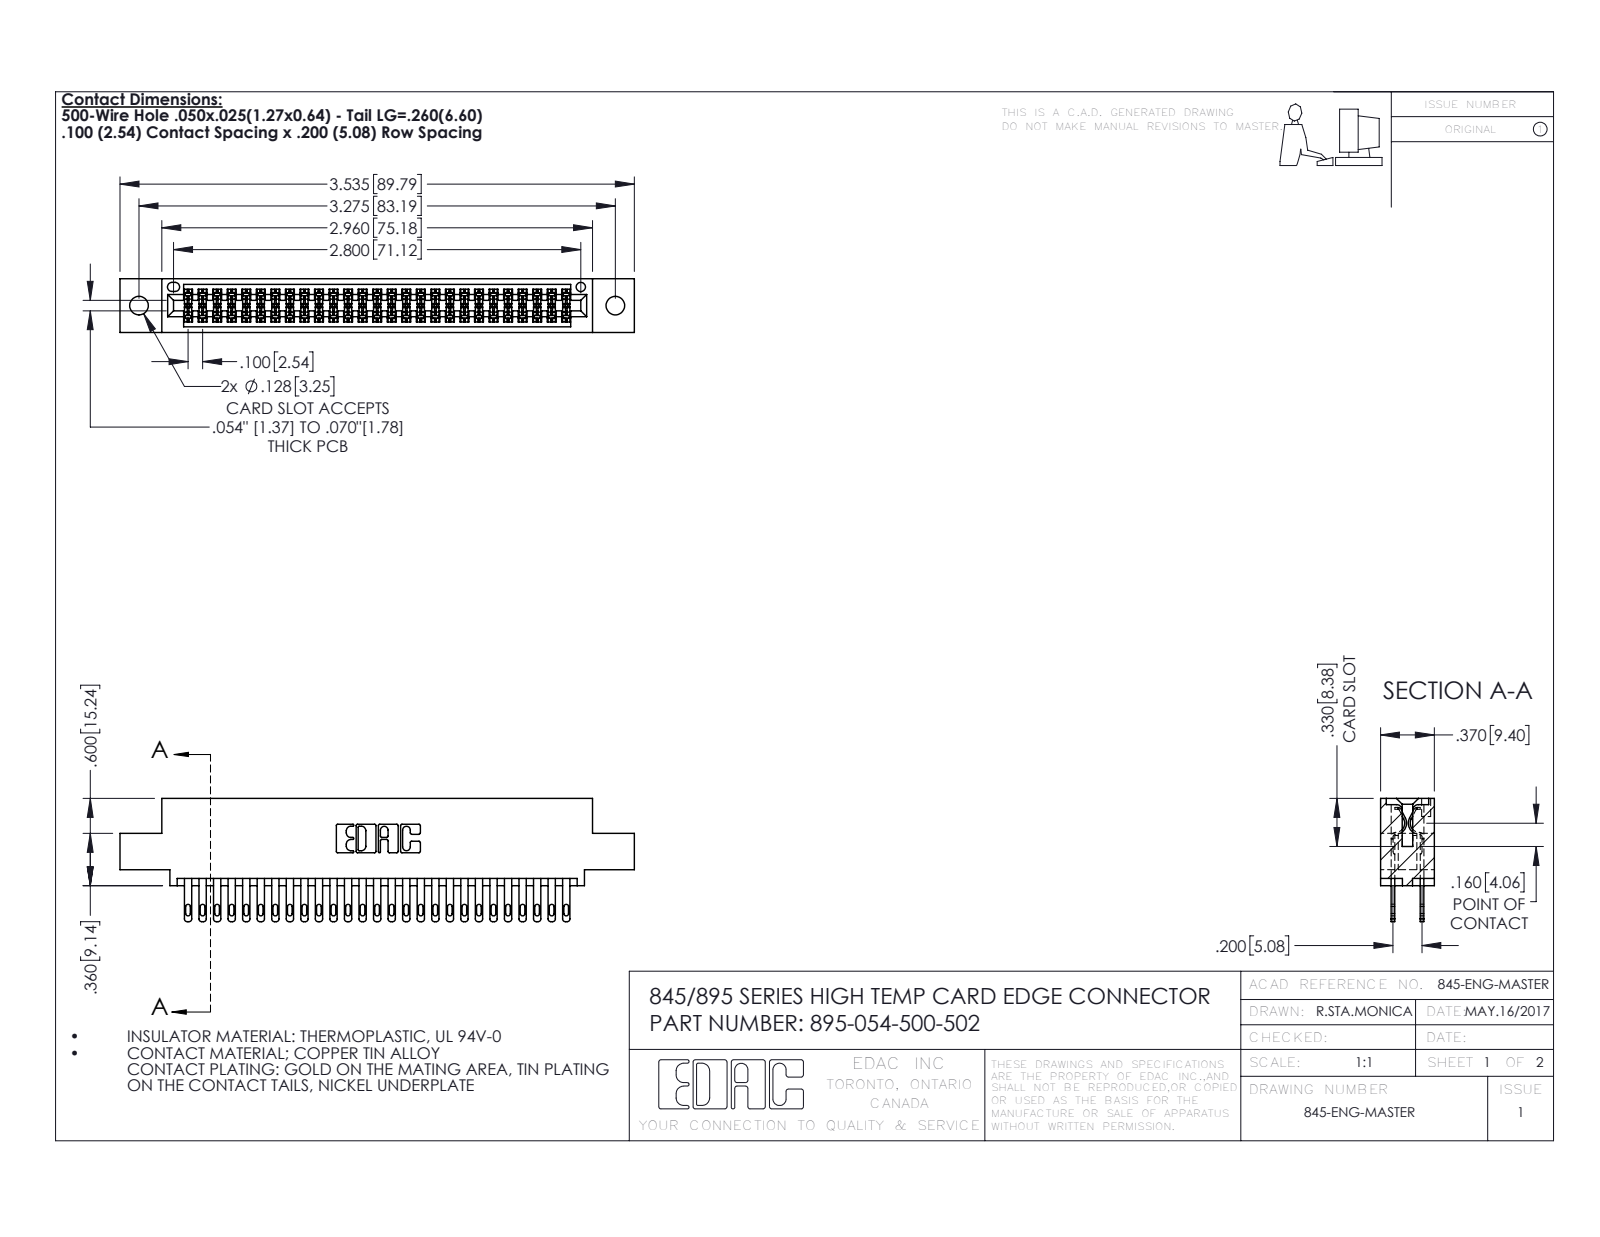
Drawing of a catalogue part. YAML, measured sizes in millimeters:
part_name: "845 Part_0.110 Offset - 0.128 Dia; 345-292-001_345-293-100; 895-054-500-502"
step_written_by: "SolidWorks 2020 (CONFIG_CONTROL_DESIGN)"
units: millimeters
bodies: {solids: 55, faces: 2614, planar: 1542, cylindrical: 1072, other: 0}
overall_size: [89.8, 21.5, 9.4]
volume: 8640
surface_area: 12850
round_holes:
  - {diameter: 3.3, count: 2}
  - {diameter: 1.6, count: 1}
partial_cylinders:
  - {radius: 0.2, count: 81}
  - {radius: 0.4, count: 54}
  - {radius: 0.5, count: 54}
  - {radius: 0.3, count: 22}
  - {radius: 0.2, count: 6}
  - {radius: 0.8, count: 6}
  - {radius: 0.7, count: 3}
  - {radius: 0.4, count: 2}
face_to_face_distances: [7.6, 1.8, 5.1, 2.5, 6.9, 0.6, 9.4, 5.7, 4.4, 3.8]
hole_center_spacings: [6.9, 77.2, 83.2]
